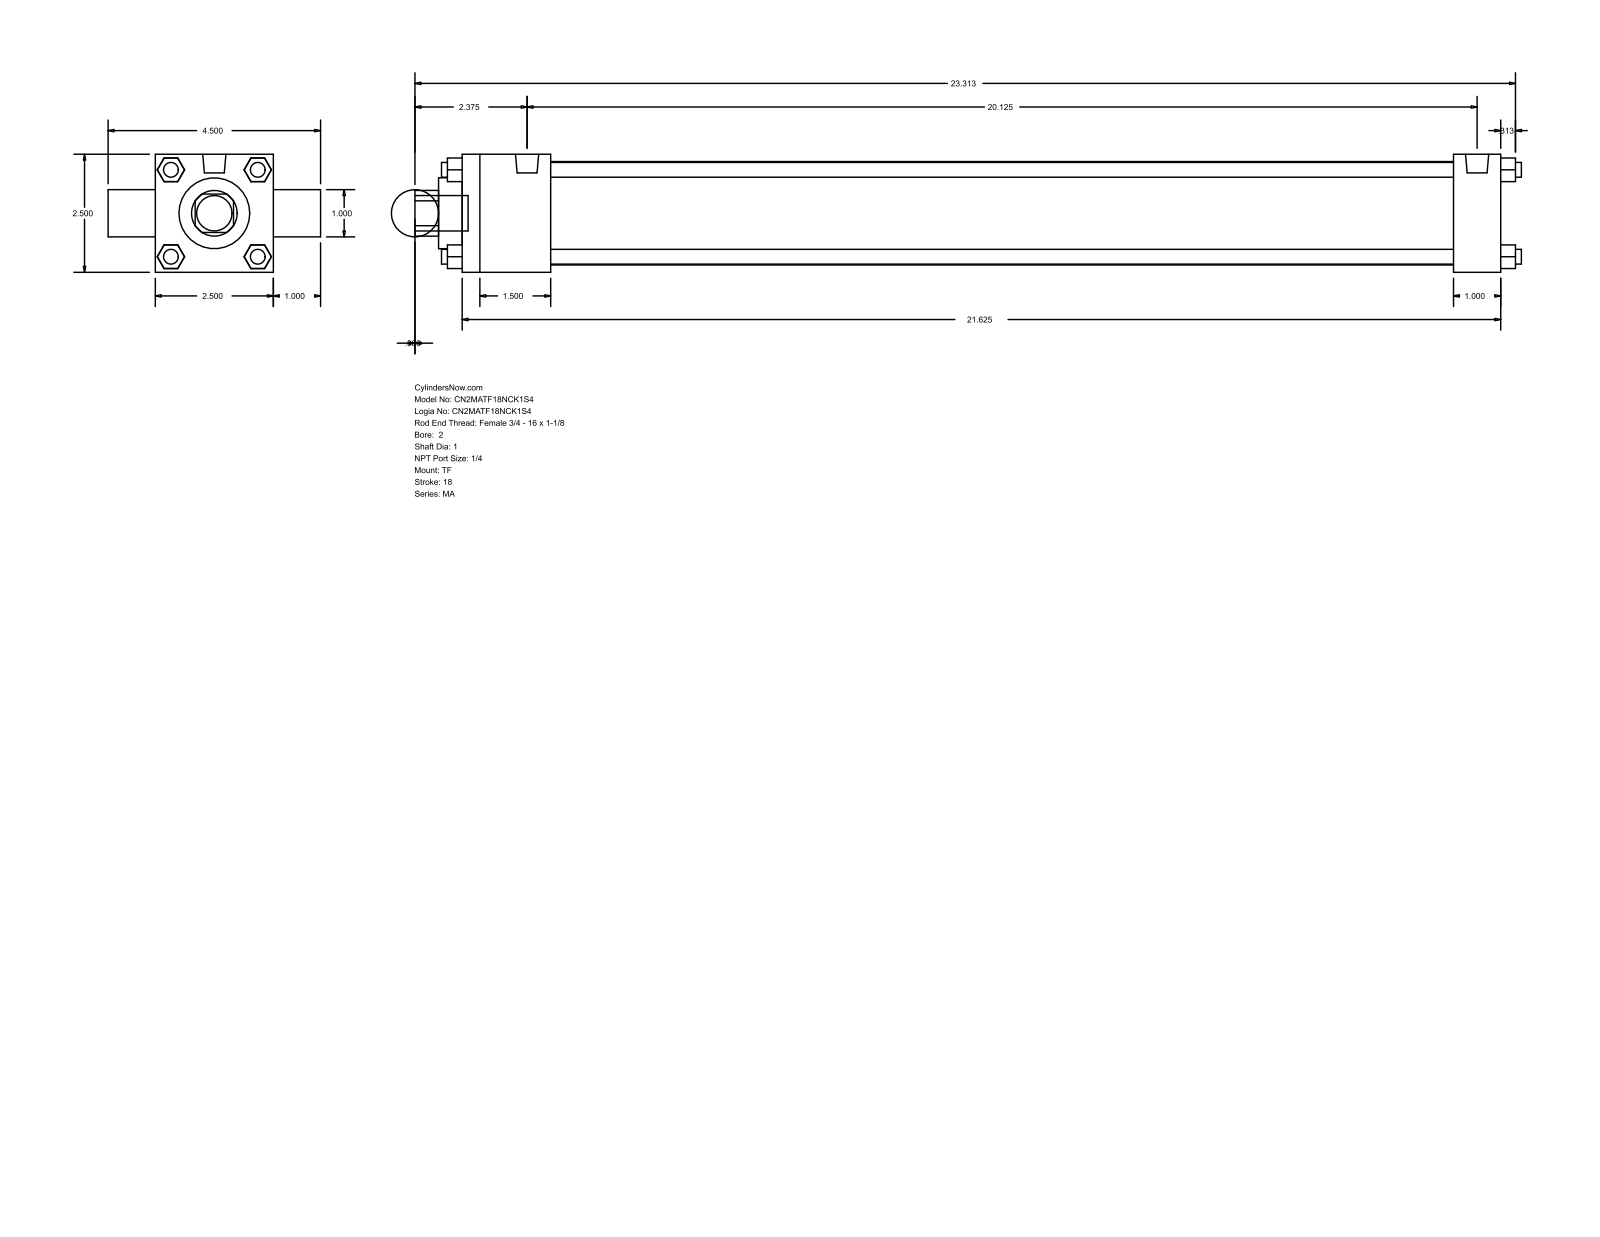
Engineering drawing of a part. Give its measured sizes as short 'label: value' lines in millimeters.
name: MA_TF__0200_1
written by: GSSL Pune (CONFIG_CONTROL_DESIGN)
unit: mm
bodies: 0 solids, 120 faces (92 planar, 28 cylindrical, 0 other)
size: 595.31 × 114.3 × 63.5
holes: 2× ⌀25.4, 1× ⌀38.1, 1× ⌀55.63
bosses: 7× ⌀7.94, 2× ⌀12.49, 1× ⌀19.05
rounds: 1× R12.29
face distances: 63.5, 25.4, 558.8, 12.7, 47.63, 533.4, 485.77, 511.17, 88.9, 23.37
